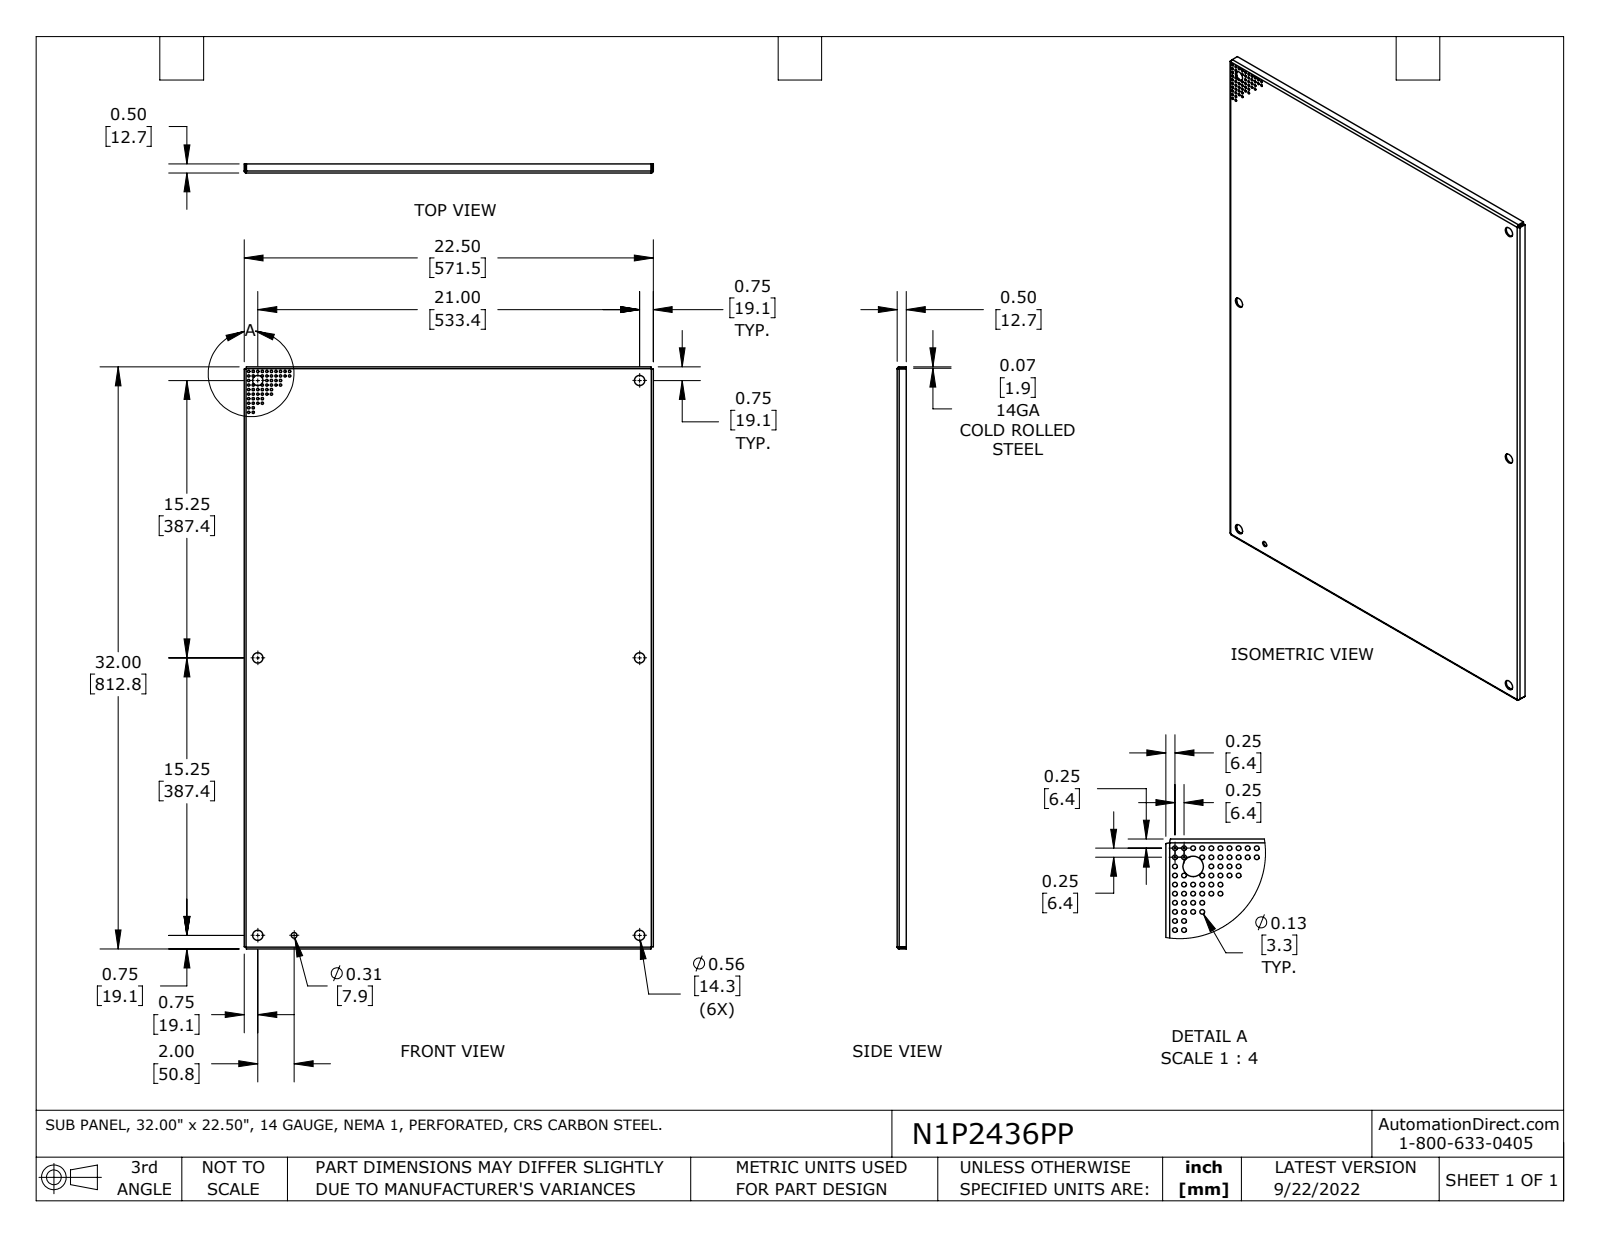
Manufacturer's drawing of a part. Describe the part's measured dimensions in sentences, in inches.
The part is named "N1P2436PP". Its 3-D file was written by "SolidWorks 2021 (AUTOMOTIVE_DESIGN)". It is 1 solid with 162 faces: 22 planar, 132 cylindrical and 8 other. Overall it measures 32 by 22.5 by 0.5 inches. Its volume is 56.28 cubic inches and its surface area 1 532 square inches. Round holes: 55 of diameter 0.13, 6 of diameter 0.563, 1 of diameter 0.312. Partial cylindrical surfaces (rounded edges, fillets, slot ends): 4 of radius 0.031, 4 of radius 0.105. The main face-to-face distances are 0.074, 22.426, 31.926, 22.352, 22.5, 32, 31.852, 0.426, 0.5, 0.126. The hole center spacings are 0.25, 0.559, 1.25, 0.791, 0.5, 1.031, 0.354, 0.902.
